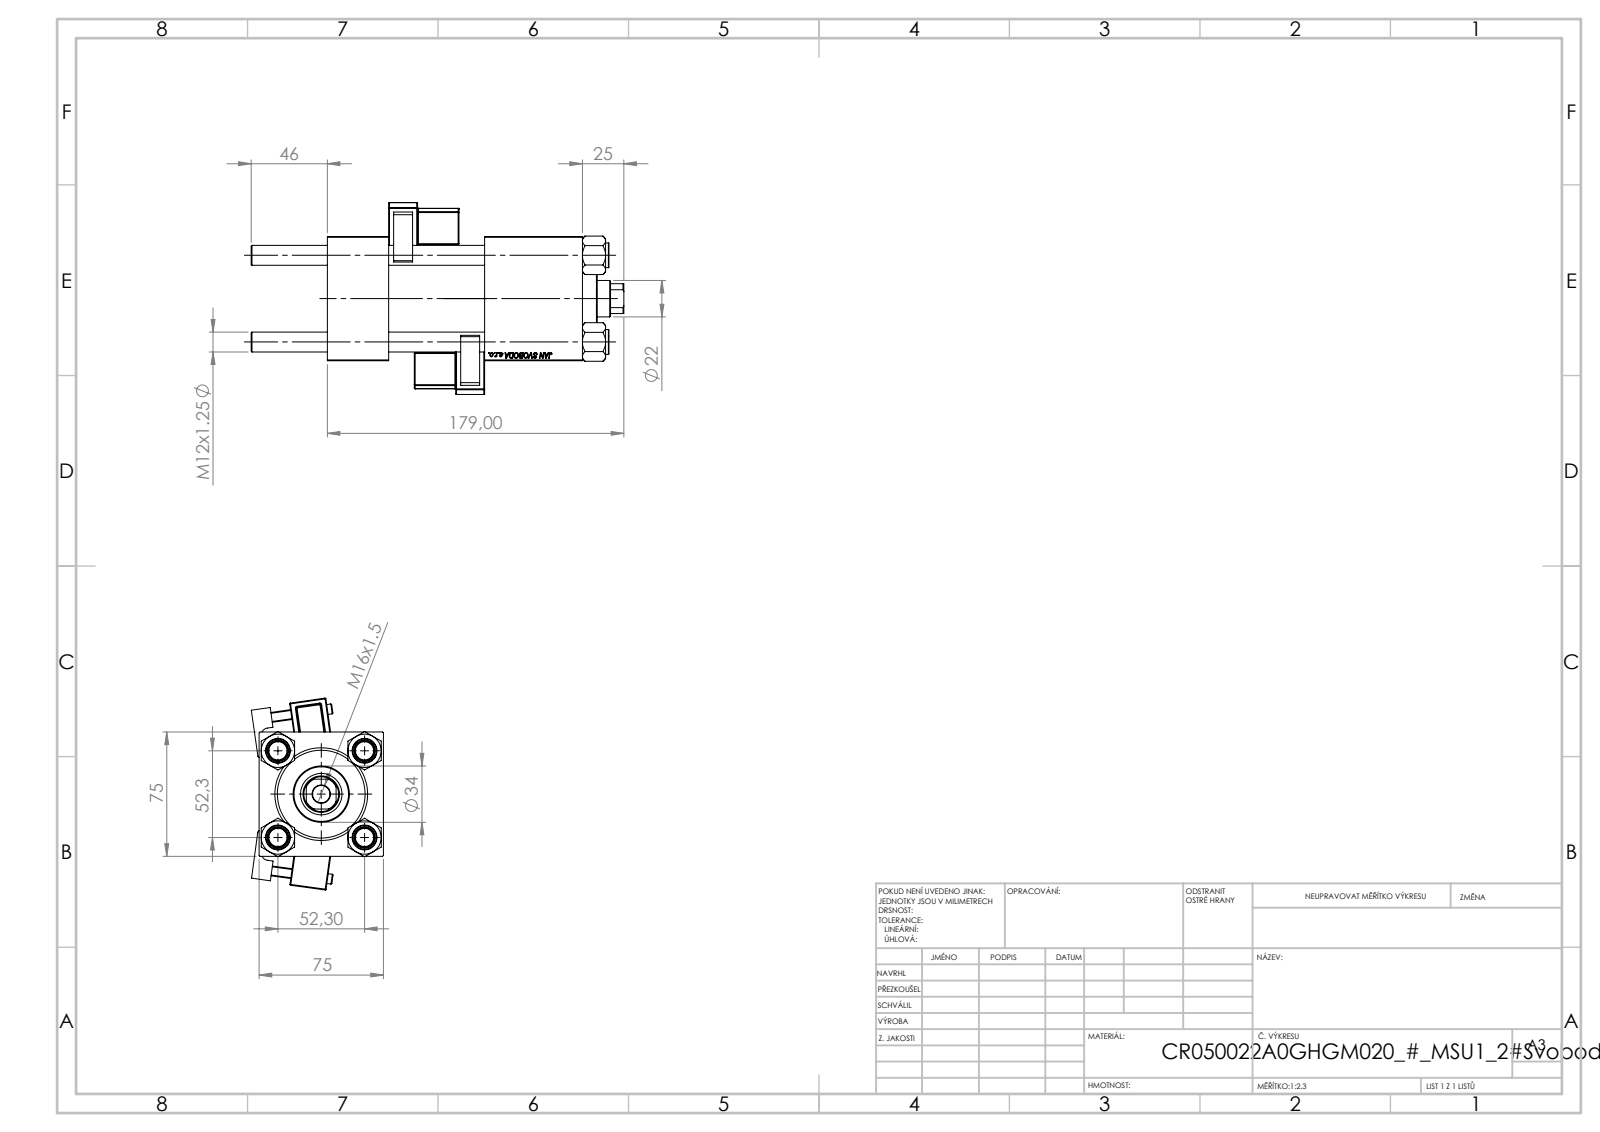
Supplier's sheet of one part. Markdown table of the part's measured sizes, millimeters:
| quantity | value |
| --- | --- |
| part name | CR025_012_A_0_G_A_G_M_020_+#_##_TYCINKA; V215CR_VCP; V215CR_MSU; V215CR_BODY_A (+2 more) |
| STEP written by | SolidWorks 2019 (CONFIG_CONTROL_DESIGN) |
| units | millimeters |
| bodies | 13 solids, 1288 faces (578 planar, 138 cylindrical, 572 other) |
| overall size | 225 × 115.75 × 79.69 |
| volume | 731 236 mm³ |
| surface area | 176 011 mm² |
| round holes (diameter × count) | 12 × 4, 7 × 2, 20.96 × 2, 30 × 2, 10.5 × 1, 22 × 1, 25 × 1, 41 × 1, 50 × 1, 53 × 1 |
| round bosses / shafts (diameter × count) | 15 × 4, 6 × 2, 56 × 1, 34 × 1 |
| partial cylindrical surfaces (radius × count) | 0.5 × 48, 1 × 2, 2.5 × 2, 4 × 2, 10.5 × 1 |
| main face-to-face distances | 75, 37, 154, 117, 95, 58, 59, 125.3, 88.3, 30.3 |
| hole center spacings | 36.98, 52.3, 73.96, 93.5 |
